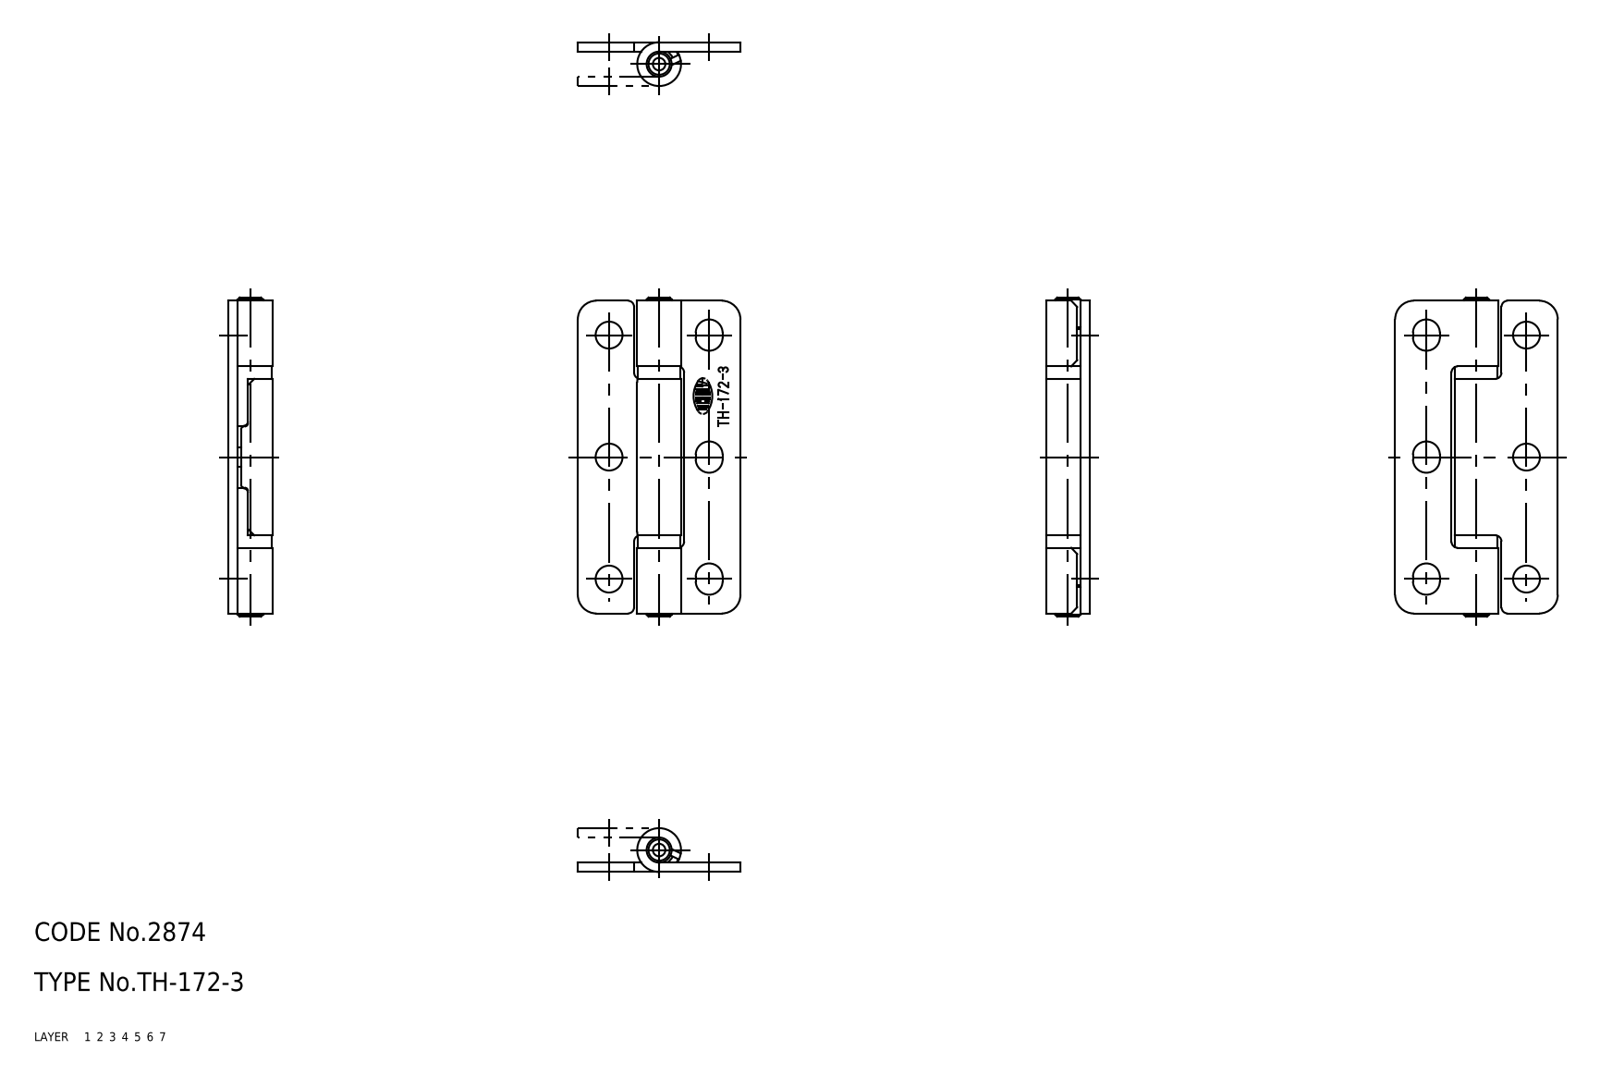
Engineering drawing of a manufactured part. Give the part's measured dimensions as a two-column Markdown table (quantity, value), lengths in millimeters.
| quantity | value |
| --- | --- |
| part name | 67115965; 67115978; 67115991; 67116004 (+2 more) |
| STEP written by | CADfix (AUTOMOTIVE_DESIGN) |
| units | millimeters |
| bodies | 6 solids, 124 faces (0 planar, 0 cylindrical, 124 other) |
| overall size | 51 × 26 × 7 |
| volume | 3 025 mm³ |
| surface area | 5 072 mm² |
